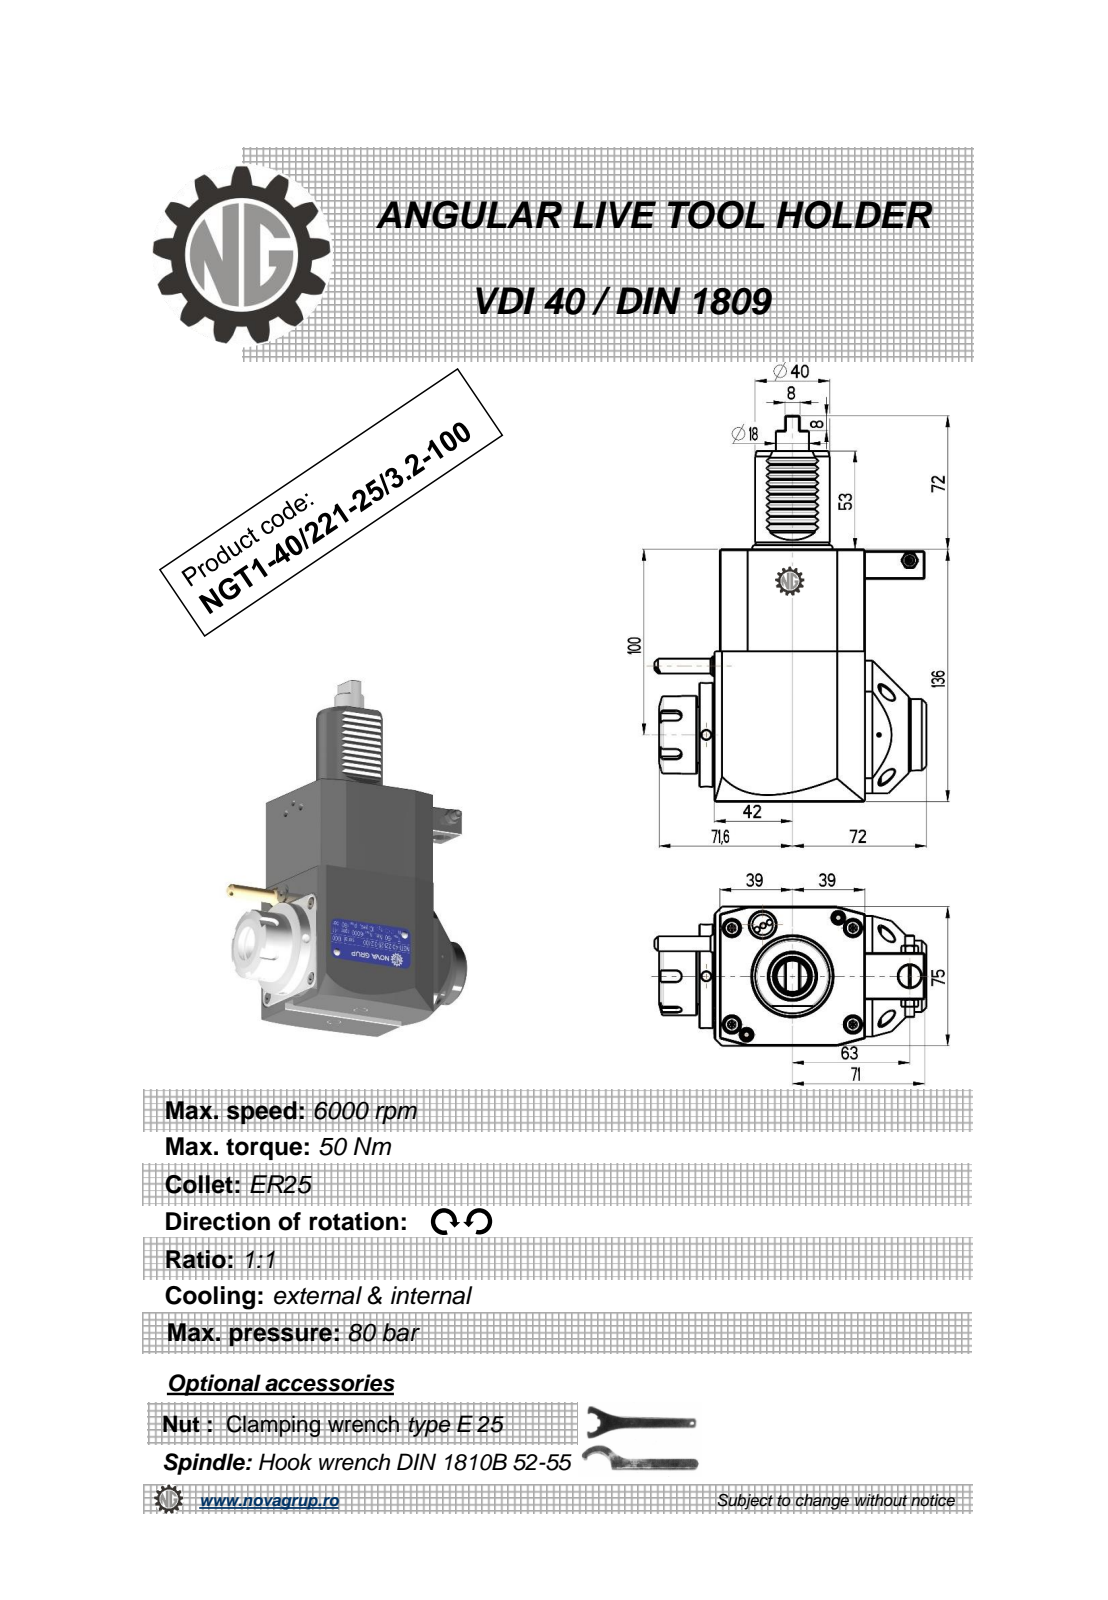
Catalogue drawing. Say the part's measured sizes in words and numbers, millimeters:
The part is named "NGT1_40_221_25_3_2_100". Its 3-D file was written by "PRO/ENGINEER BY PARAMETRIC TECHNOLOGY CORPORATION, 2010280 (CONFIG_CONTROL_DESIGN)". It is 1 solid with 430 faces: 190 planar, 91 cylindrical and 149 other. Overall it measures 208 by 146.14 by 75 millimeters. Its volume is 1 001 000 cubic millimeters and its surface area 77 439 square millimeters. Round holes: 3 of diameter 5, 1 of diameter 3, 1 of diameter 4.2, 1 of diameter 4.5, 1 of diameter 9.5, 1 of diameter 12, 1 of diameter 20.3. Round bosses or shafts: 1 of diameter 56, 1 of diameter 43, 1 of diameter 42, 1 of diameter 40, 1 of diameter 38.5, 1 of diameter 33, 1 of diameter 17.8, 1 of diameter 11.2. Partial cylindrical surfaces (rounded edges, fillets, slot ends): 12 of radius 0.26, 10 of radius 0.3, 6 of radius 0.22, 5 of radius 3, 2 of radius 0.8, 1 of radius 0.5, 1 of radius 40. The main face-to-face distances are 75, 136, 78, 81, 3, 8, 11, 84.88, 2.8, 80.8. The hole center spacings are 40.93, 58.19, 92.5, 109.25, 144.12.
